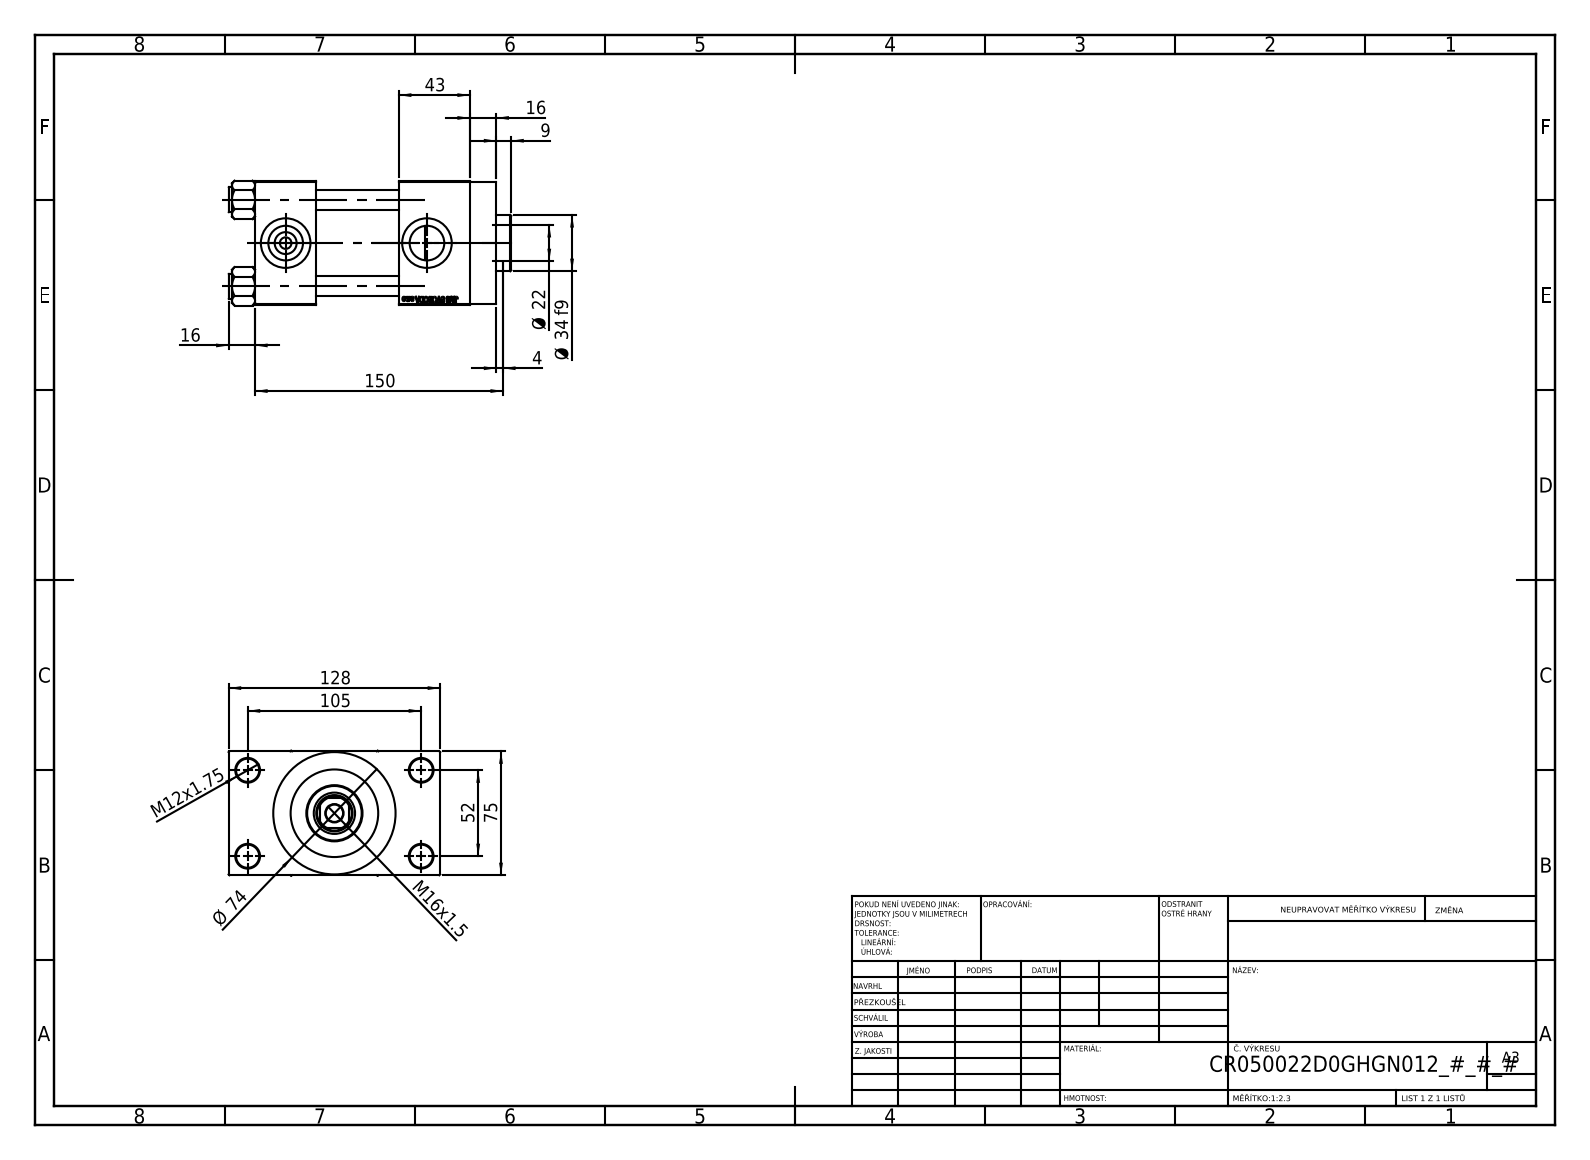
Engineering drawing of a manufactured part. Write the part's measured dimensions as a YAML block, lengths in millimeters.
part_name: "V215CR_D_Body; V215_VC_A; V215CR_D_TYCINKA; NUT_M5_D (+1 more)"
step_written_by: "SolidWorks 2019 (CONFIG_CONTROL_DESIGN)"
units: millimeters
bodies: {solids: 11, faces: 1103, planar: 497, cylindrical: 88, other: 518}
overall_size: [171, 128, 75.54]
volume: 761462
surface_area: 159844
round_holes:
  - {diameter: 12, count: 4}
  - {diameter: 14, count: 4}
  - {diameter: 7, count: 2}
  - {diameter: 20.96, count: 2}
  - {diameter: 30, count: 2}
  - {diameter: 10.5, count: 1}
  - {diameter: 22, count: 1}
  - {diameter: 25, count: 1}
  - {diameter: 41, count: 1}
  - {diameter: 50, count: 1}
  - {diameter: 53, count: 1}
round_bosses_or_shafts:
  - {diameter: 15, count: 4}
  - {diameter: 74, count: 1}
  - {diameter: 56, count: 1}
  - {diameter: 34, count: 1}
partial_cylinders:
  - {radius: 10.5, count: 1}
face_to_face_distances: [75, 50, 37, 87, 26.5, 130, 93, 43, 101.5, 16]
hole_center_spacings: [26.35, 36.98, 52.3, 58.43, 58.59, 78.65, 94.37, 52]
